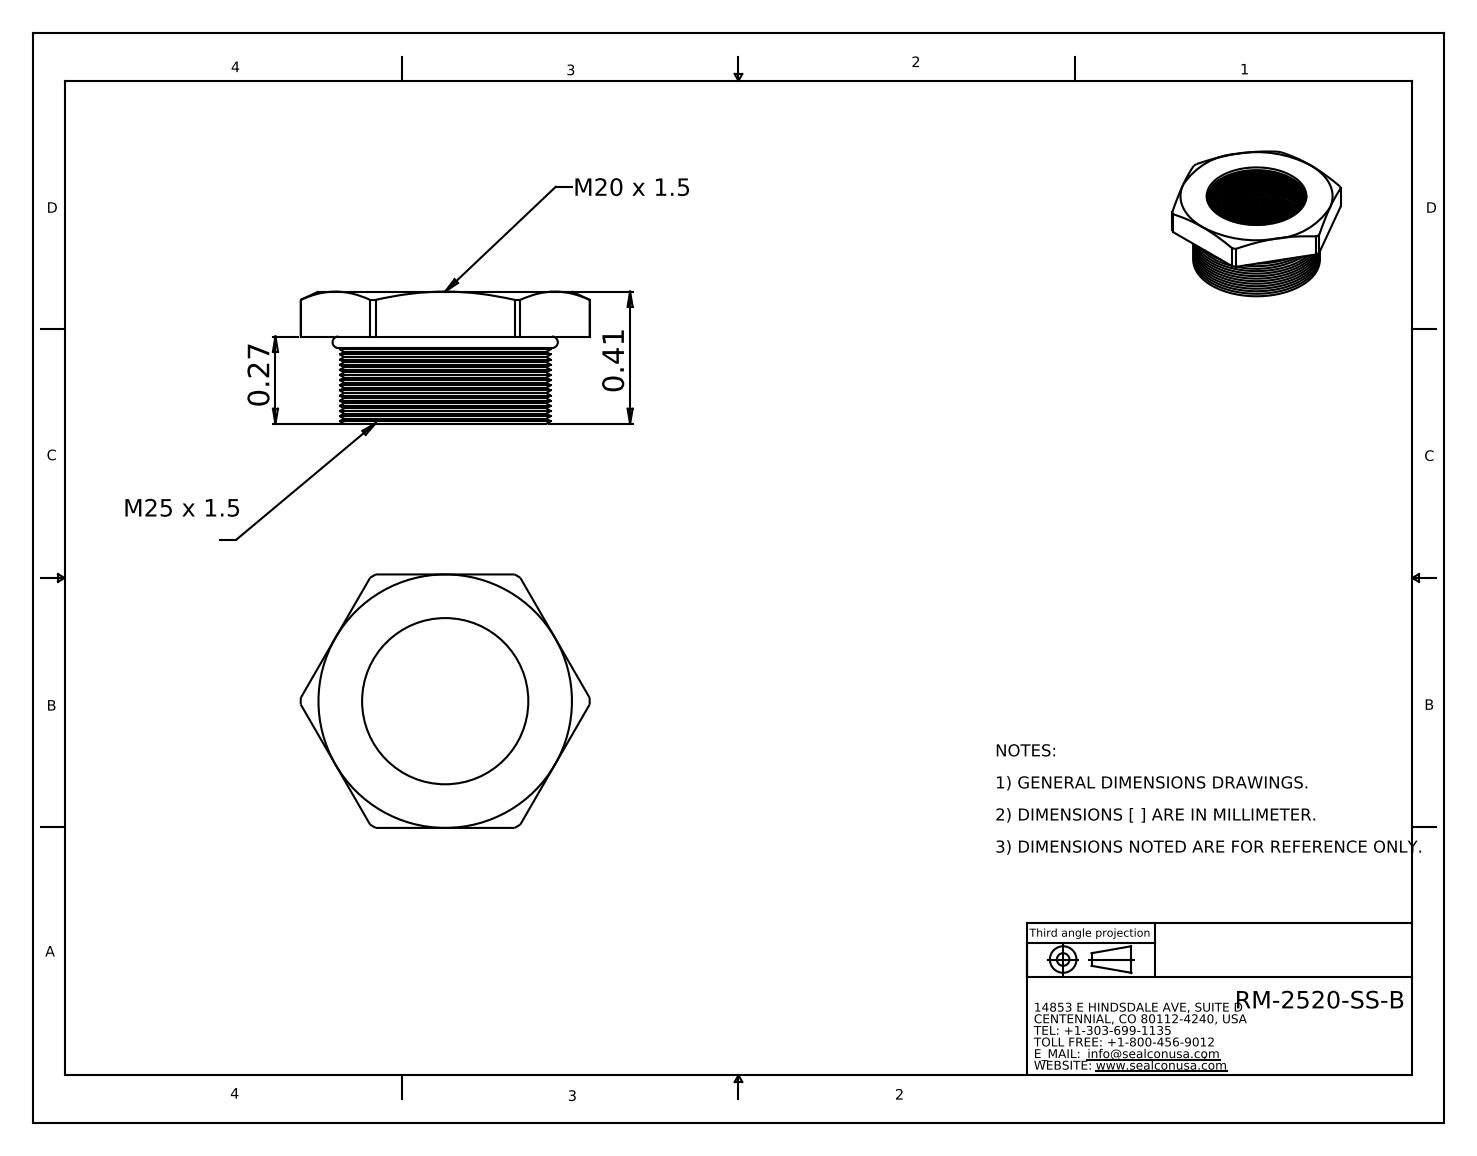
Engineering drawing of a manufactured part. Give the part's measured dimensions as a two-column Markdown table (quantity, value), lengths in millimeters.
| quantity | value |
| --- | --- |
| part name | RM-2520-SS-B |
| STEP written by | SolidWorks 2008 (CONFIG_CONTROL_DESIGN) |
| units | millimeters |
| bodies | 2 solids, 275 faces (9 planar, 91 cylindrical, 175 other) |
| overall size | 22.9 × 20.1 × 10.5 |
| volume | 1 300 mm³ |
| surface area | 2 355 mm² |
| round holes (diameter × count) | 13.2 × 1 |
| round bosses / shafts (diameter × count) | 16 × 1 |
| partial cylindrical surfaces (radius × count) | 11.4 × 1 |
| main face-to-face distances | 3.6, 20.1, 6.9, 10.4 |
